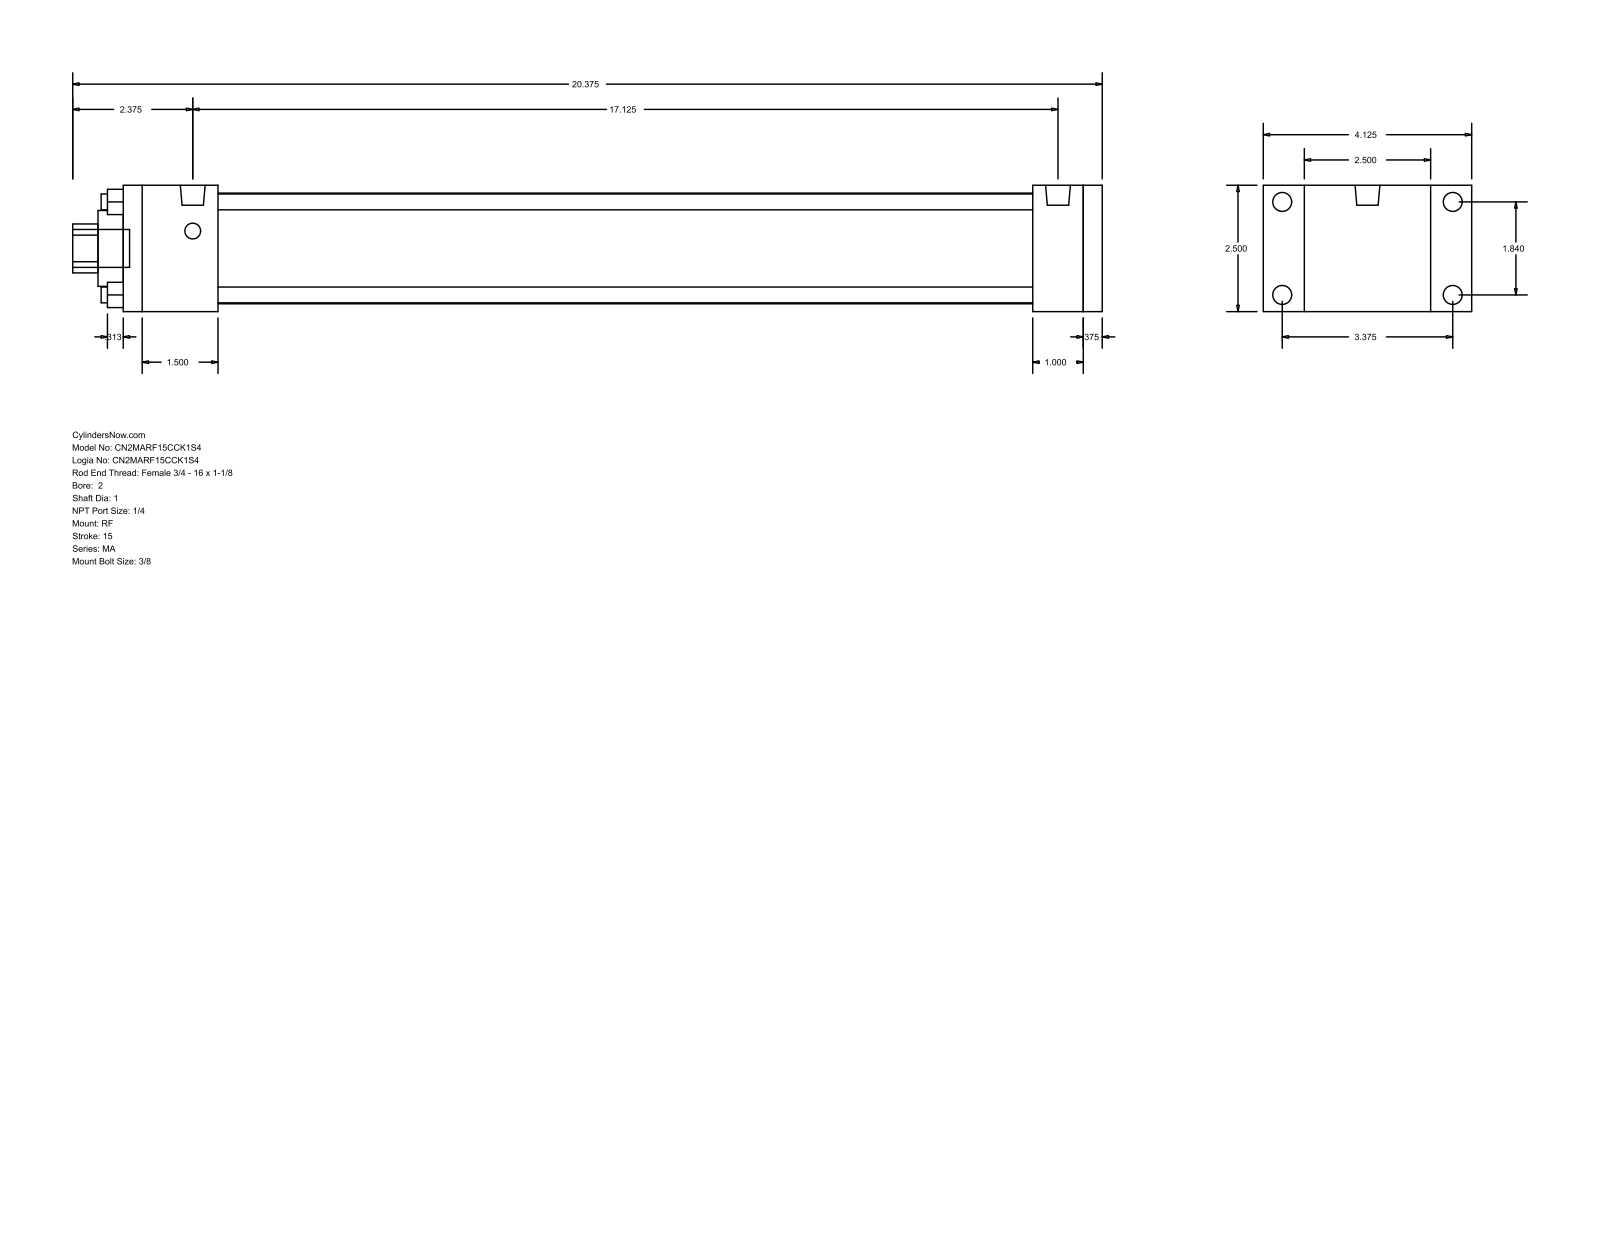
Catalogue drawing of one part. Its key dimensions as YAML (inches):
part_name: "MA_RF__0200_1"
step_written_by: "GSSL Pune (CONFIG_CONTROL_DESIGN)"
units: inches
bodies: {solids: 0, faces: 92, planar: 64, cylindrical: 28, other: 0}
overall_size: [20.375, 4.125, 2.5]
round_holes:
  - {diameter: 0.313, count: 4}
  - {diameter: 1, count: 1}
  - {diameter: 1.5, count: 1}
  - {diameter: 2.19, count: 1}
round_bosses_or_shafts:
  - {diameter: 0.375, count: 4}
  - {diameter: 0.313, count: 4}
  - {diameter: 0.492, count: 2}
  - {diameter: 0.75, count: 1}
partial_cylinders:
  - {radius: 0.484, count: 1}
face_to_face_distances: [2.5, 19, 0.375, 19.375, 1, 0.813, 0.5, 1.875, 17.125, 17.5]
hole_center_spacings: [1.301, 1.84, 2.602]
